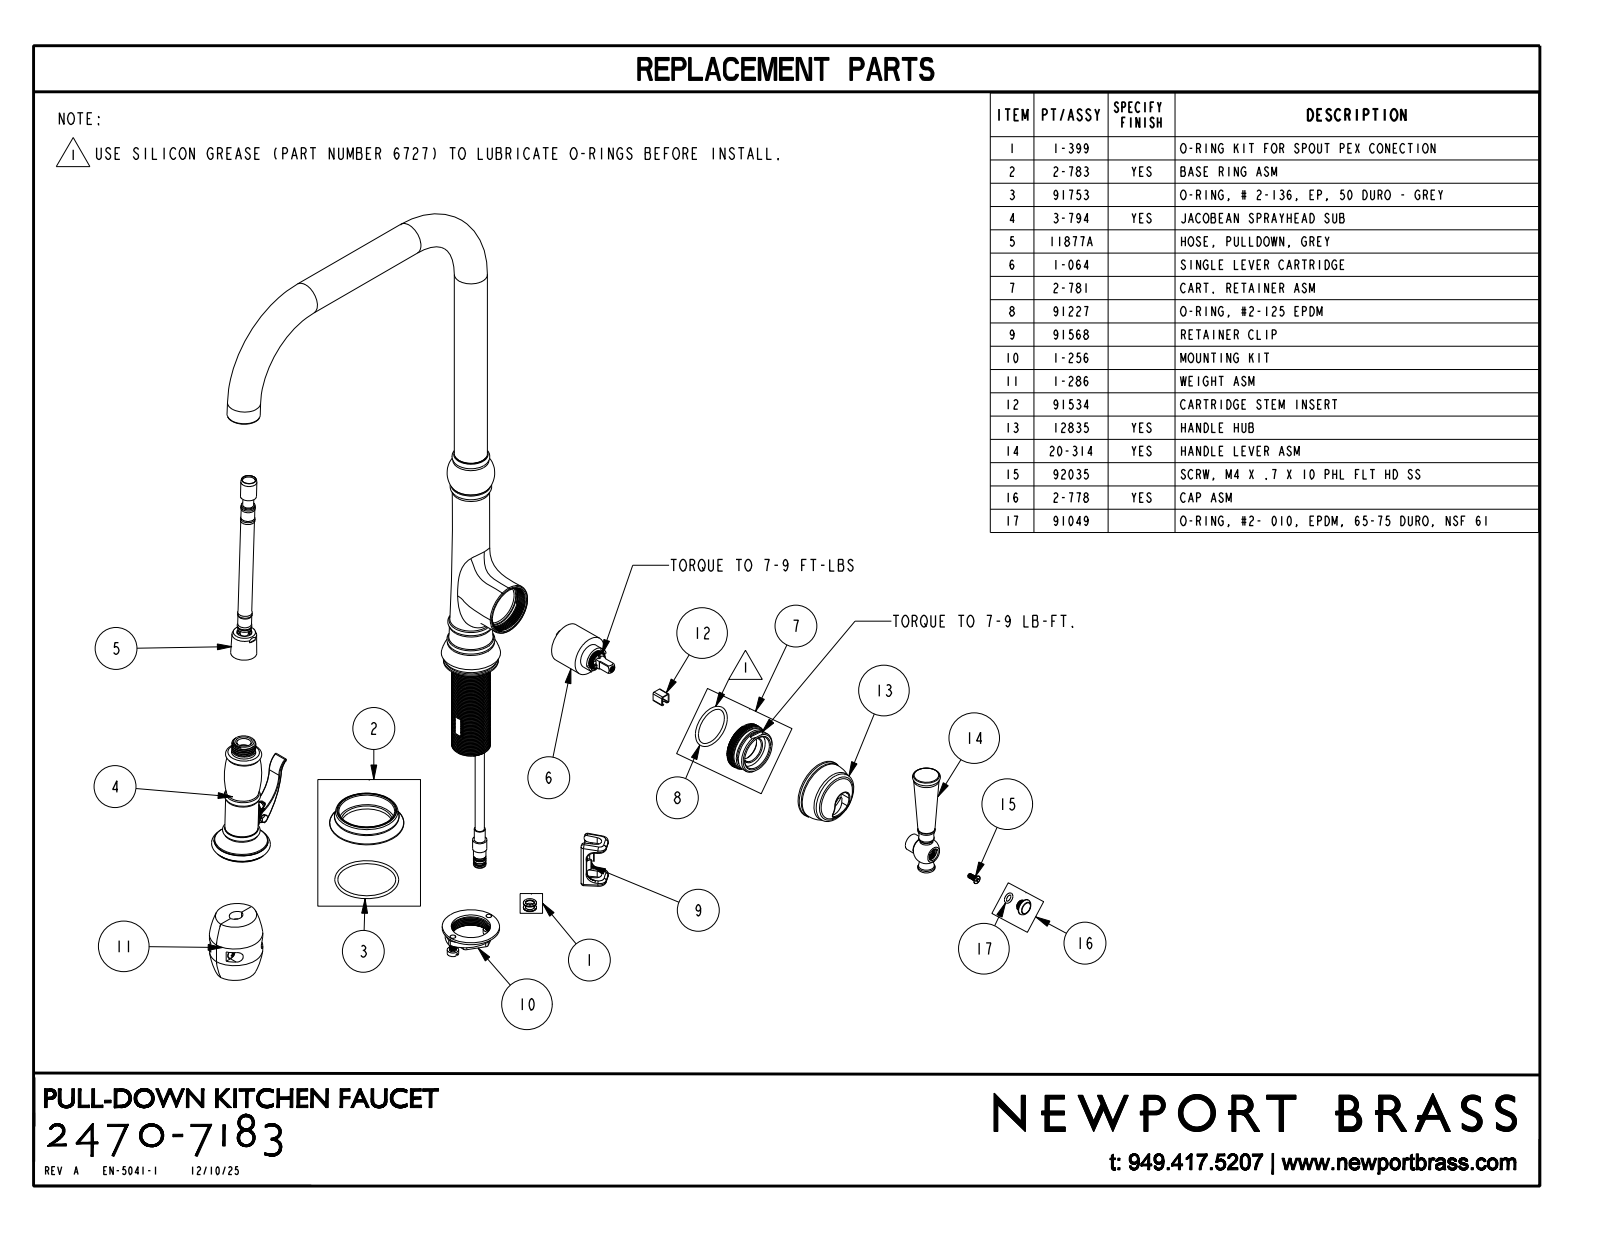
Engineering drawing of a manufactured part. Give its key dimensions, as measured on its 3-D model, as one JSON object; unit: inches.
{"part_name": "2470-7183", "step_written_by": "CREO PARAMETRIC BY PTC INC, 2025093 (CONFIG_CONTROL_DESIGN)", "units": "inches", "bodies": {"solids": 4, "faces": 475, "planar": 67, "cylindrical": 135, "other": 273}, "overall_size": [20.048, 13.464, 4.909], "volume_in3": 50.77, "surface_area_in2": 182.2, "round_holes": [[0.228, 1]], "round_bosses_or_shafts": [[0.102, 18], [2.02, 1], [1.855, 1], [1.142, 1], [0.839, 1], [0.595, 1], [0.56, 1], [0.45, 1]], "partial_cylinders_radius": [[0.02, 16], [0.03, 15], [0.065, 12], [0.025, 7], [0.06, 5], [0.045, 4], [0.337, 2], [0.04, 1]], "face_to_face_distances": [0.015, 3.959, 8.928, 8.913, 3.933, 0.025, 0.795, 3.937, 3.962, 1.87]}
